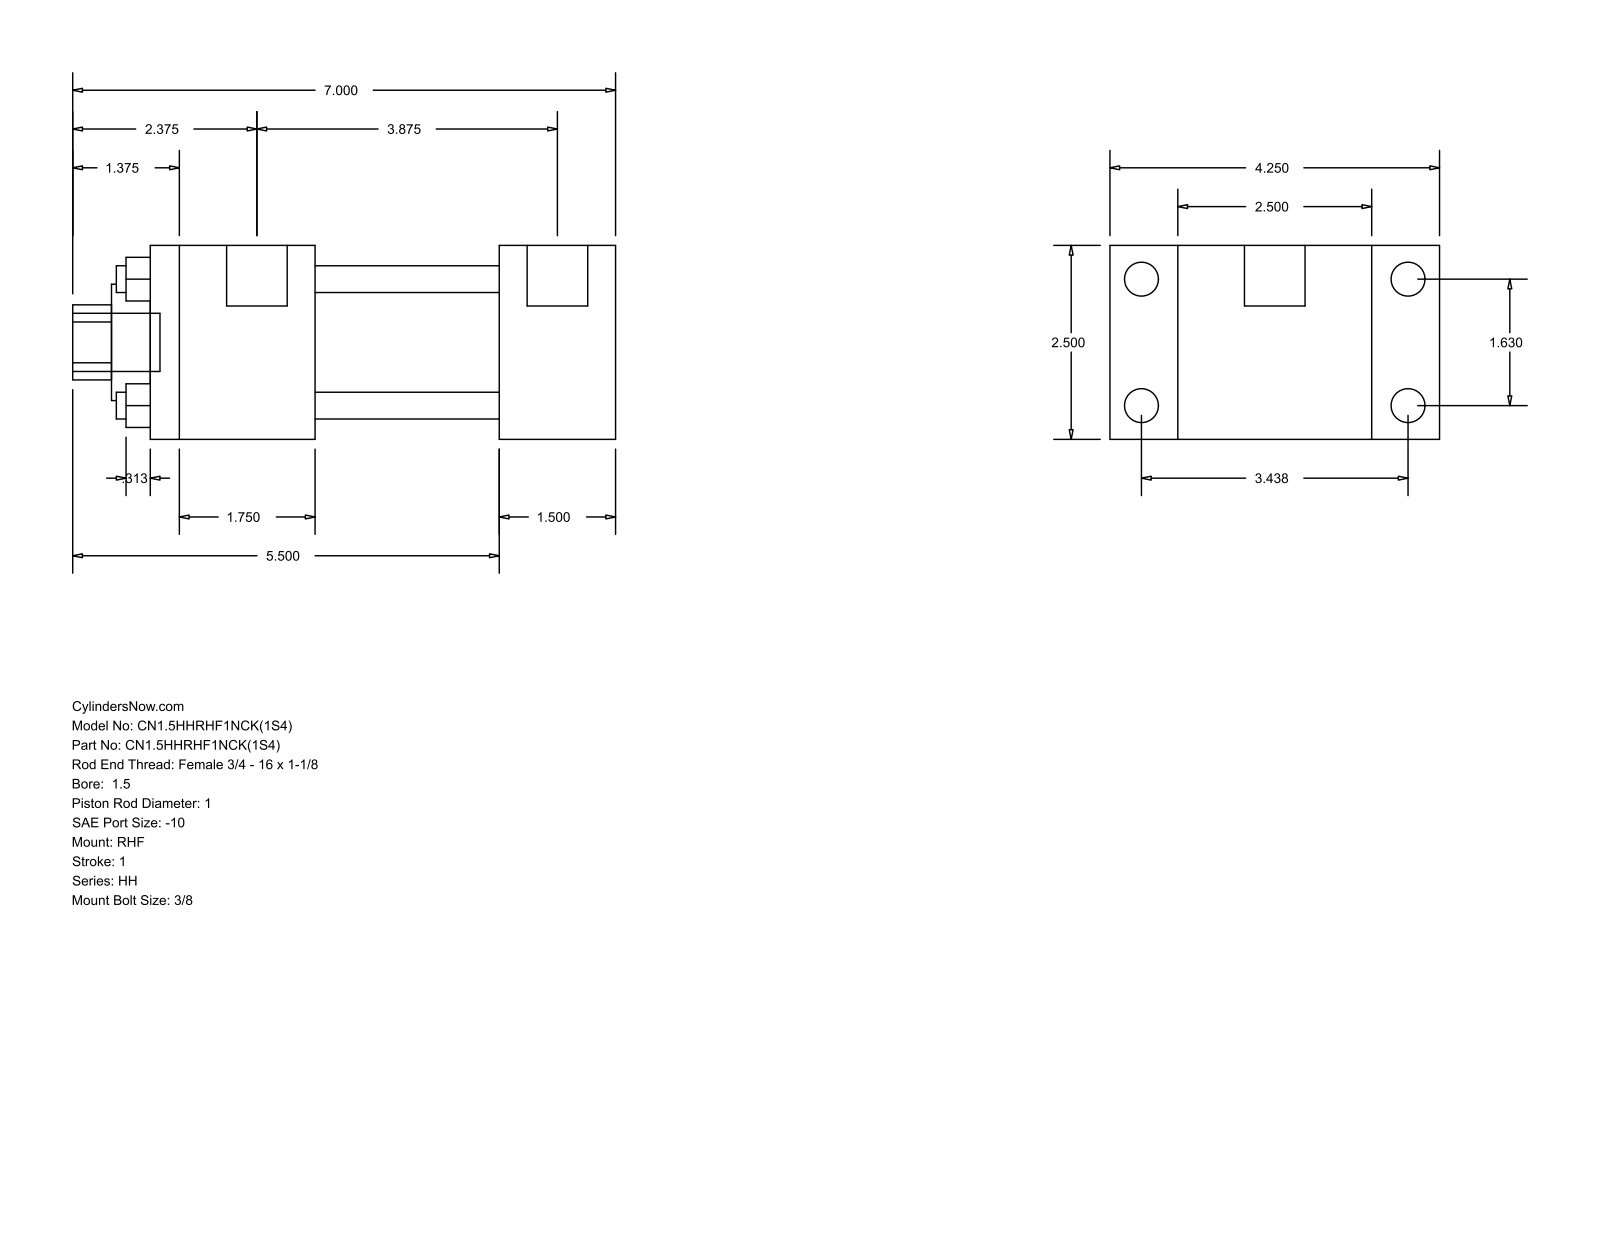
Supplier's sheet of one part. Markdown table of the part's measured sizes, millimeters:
| quantity | value |
| --- | --- |
| part name | HH_RHF__0150_1 |
| STEP written by | GSSL Pune (CONFIG_CONTROL_DESIGN) |
| units | millimeters |
| bodies | 0 solids, 88 faces (60 planar, 28 cylindrical, 0 other) |
| overall size | 177.8 × 107.95 × 63.5 |
| round holes (diameter × count) | 8.76 × 4, 25.4 × 1, 38.1 × 1, 44.45 × 1 |
| round bosses / shafts (diameter × count) | 11.13 × 4, 5.56 × 4, 19.84 × 2, 19.05 × 1 |
| partial cylindrical surfaces (radius × count) | 12.29 × 1 |
| main face-to-face distances | 63.5, 22.23, 85.73, 38.1, 107.96, 60.32, 98.42, 53.98, 114.3, 152.4 |
| hole center spacings | 29.27, 41.4, 58.55 |
